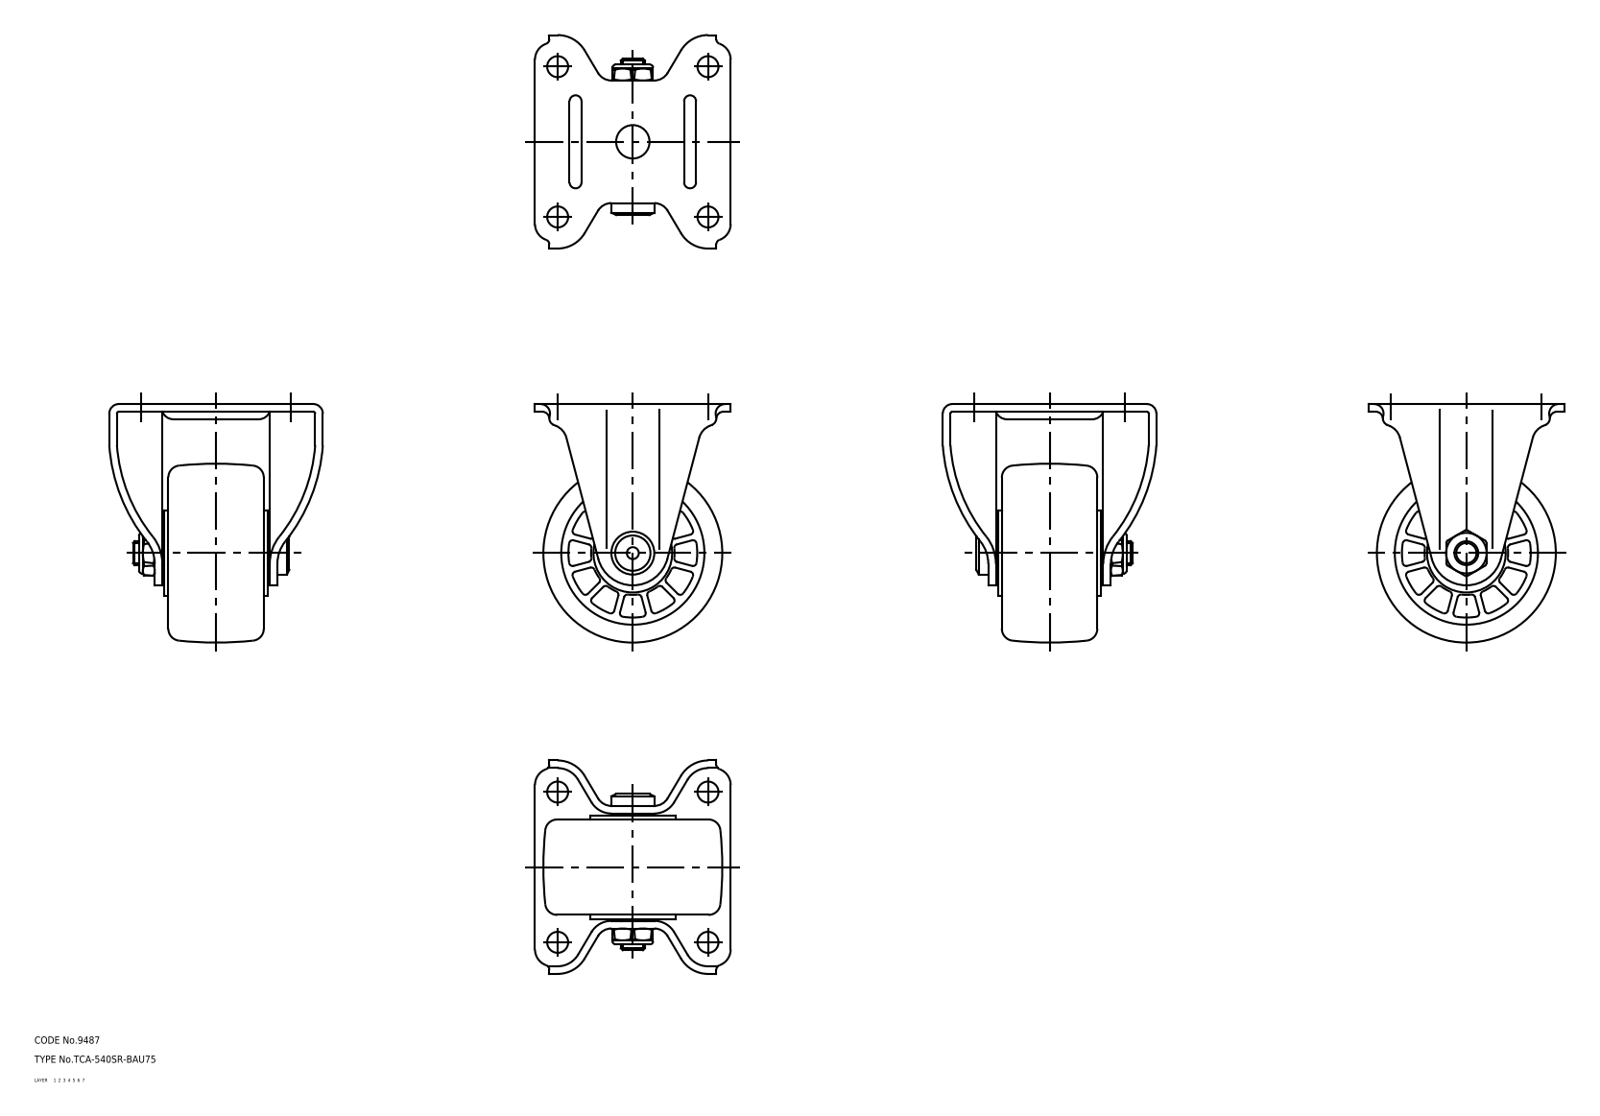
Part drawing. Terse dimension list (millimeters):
name: wheel; axle; No_540SR_BAU75_1144_36
written by: CADfix (AUTOMOTIVE_DESIGN)
unit: mm
bodies: 3 solids, 335 faces (0 planar, 0 cylindrical, 335 other)
size: 100 × 89.5 × 82
volume: 177 708 mm³; area: 65 176 mm²
